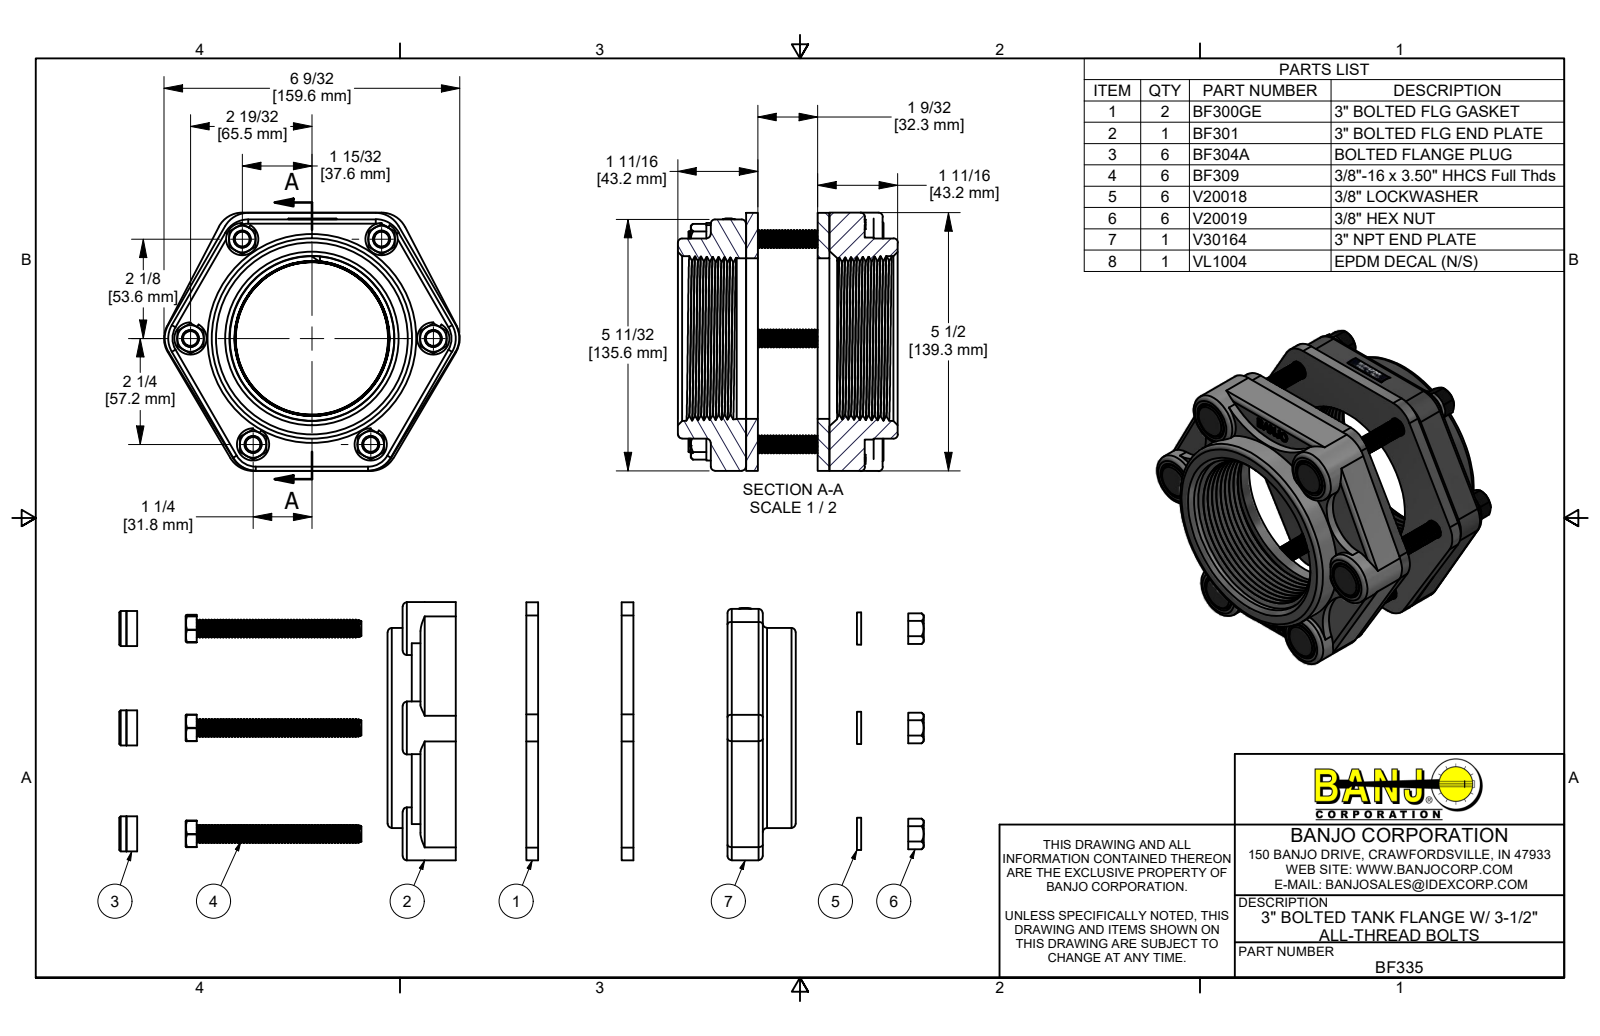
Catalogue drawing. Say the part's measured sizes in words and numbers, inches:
The part is named "BF335; BF301; BF300GE; V30164 (+5 more)". Its 3-D file was written by "Autodesk Inventor 2019 (AUTOMOTIVE_DESIGN)". It is 29 solids with 2443 faces: 448 planar, 949 cylindrical and 1046 other. Overall it measures 6.285 by 5.485 by 4.673 inches. Its volume is 44.43 cubic inches and its surface area 327.7 square inches. Round holes: 6 of diameter 0.307, 6 of diameter 0.385, 6 of diameter 0.406, 6 of diameter 0.406, 6 of diameter 0.41, 6 of diameter 0.715, 6 of diameter 0.75, 1 of diameter 3.41. Round bosses or shafts: 330 of diameter 0.324, 6 of diameter 1.125, 6 of diameter 0.742, 6 of diameter 0.687, 6 of diameter 0.375, 1 of diameter 4.25. Partial cylindrical surfaces (rounded edges, fillets, slot ends): 18 of radius 0.09, 12 of radius 0.162, 6 of radius 0.322, 6 of radius 0.56, 6 of radius 0.562, 2 of radius 0.794, 2 of radius 1.094, 1 of radius 0.517. The main face-to-face distances are 0.25, 1.523, 1.773, 1.273, 0.75, 1, 2.273, 2.523, 2.973, 0.7. The hole center spacings are 2.38, 2.574, 2.577, 2.58, 2.614, 4.366, 4.442, 4.575.
